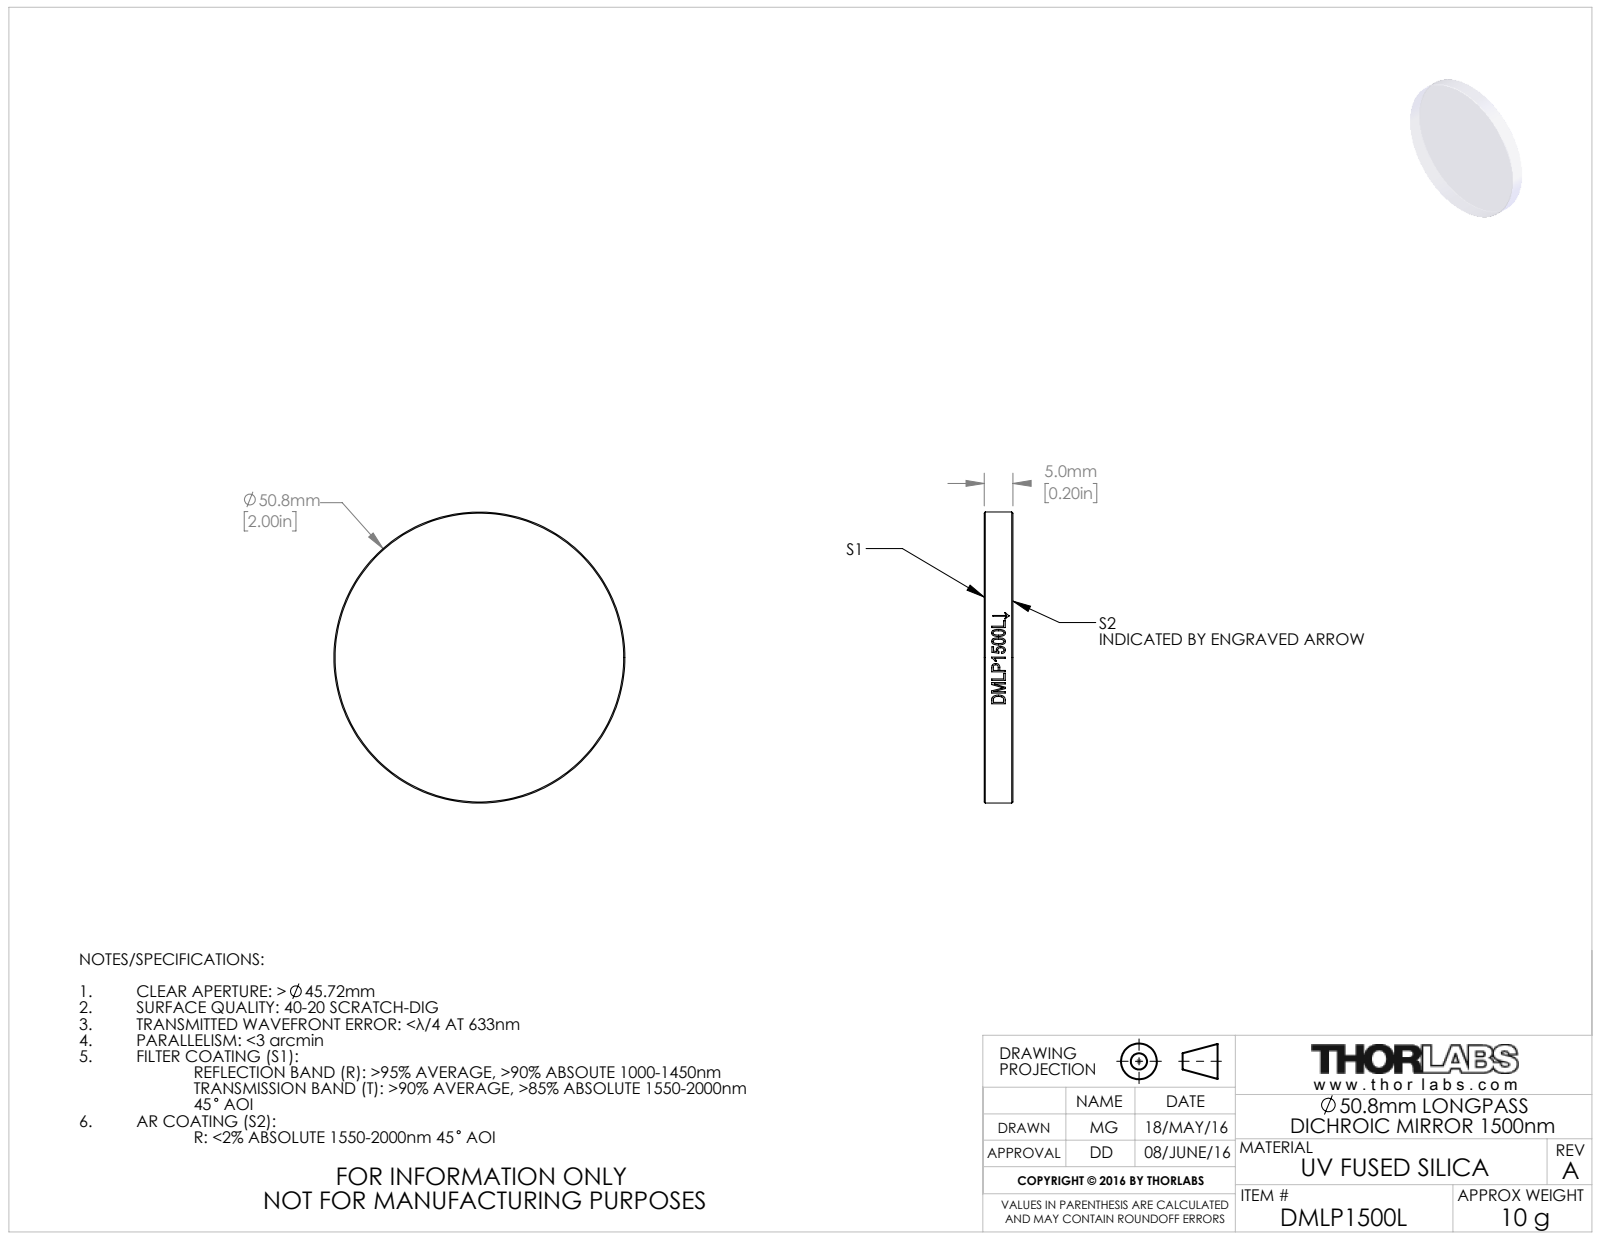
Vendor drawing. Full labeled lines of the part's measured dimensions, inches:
Part name (STEP PRODUCT): TTN045173-E0W
STEP written by: SolidWorks 2016 (CONFIG_CONTROL_DESIGN)
Units: inches
Bodies: 1 solid, 22 faces (2 planar, 16 cylindrical, 4 other)
Overall size (bounding box): 2 × 2 × 0.197
Volume: 0.618 in³ · Surface area: 7.462 in²
Round bosses / shafts (diameter × count): ⌀2 ×1
Main face-to-face distances: 0.197
